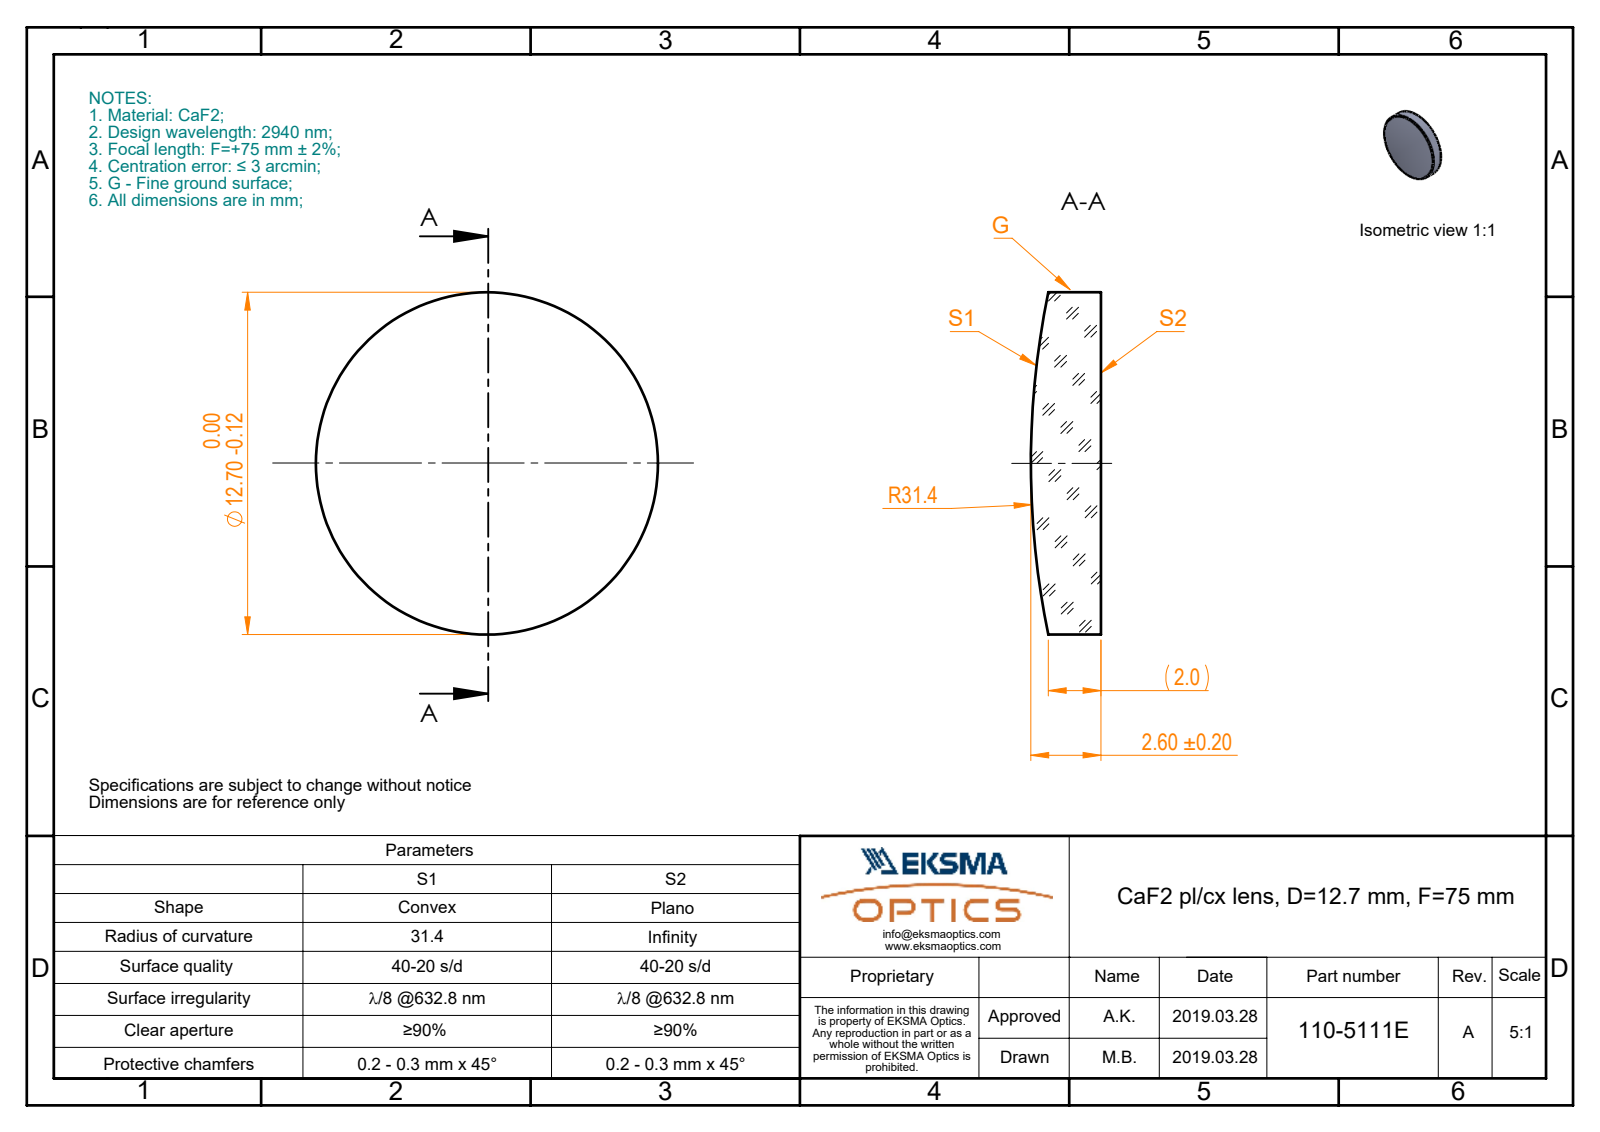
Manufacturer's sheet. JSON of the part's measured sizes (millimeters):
{"part_name": "110-5111E CaF2 pl-cx 12.7 F75", "step_written_by": "SolidWorks 2017 (CONFIG_CONTROL_DESIGN)", "units": "millimeters", "bodies": {"solids": 1, "faces": 5, "planar": 1, "cylindrical": 2, "other": 2}, "overall_size": [12.7, 12.7, 2.6], "volume_mm3": 288, "surface_area_mm2": 332, "round_bosses_or_shafts": [[12.7, 1]]}
